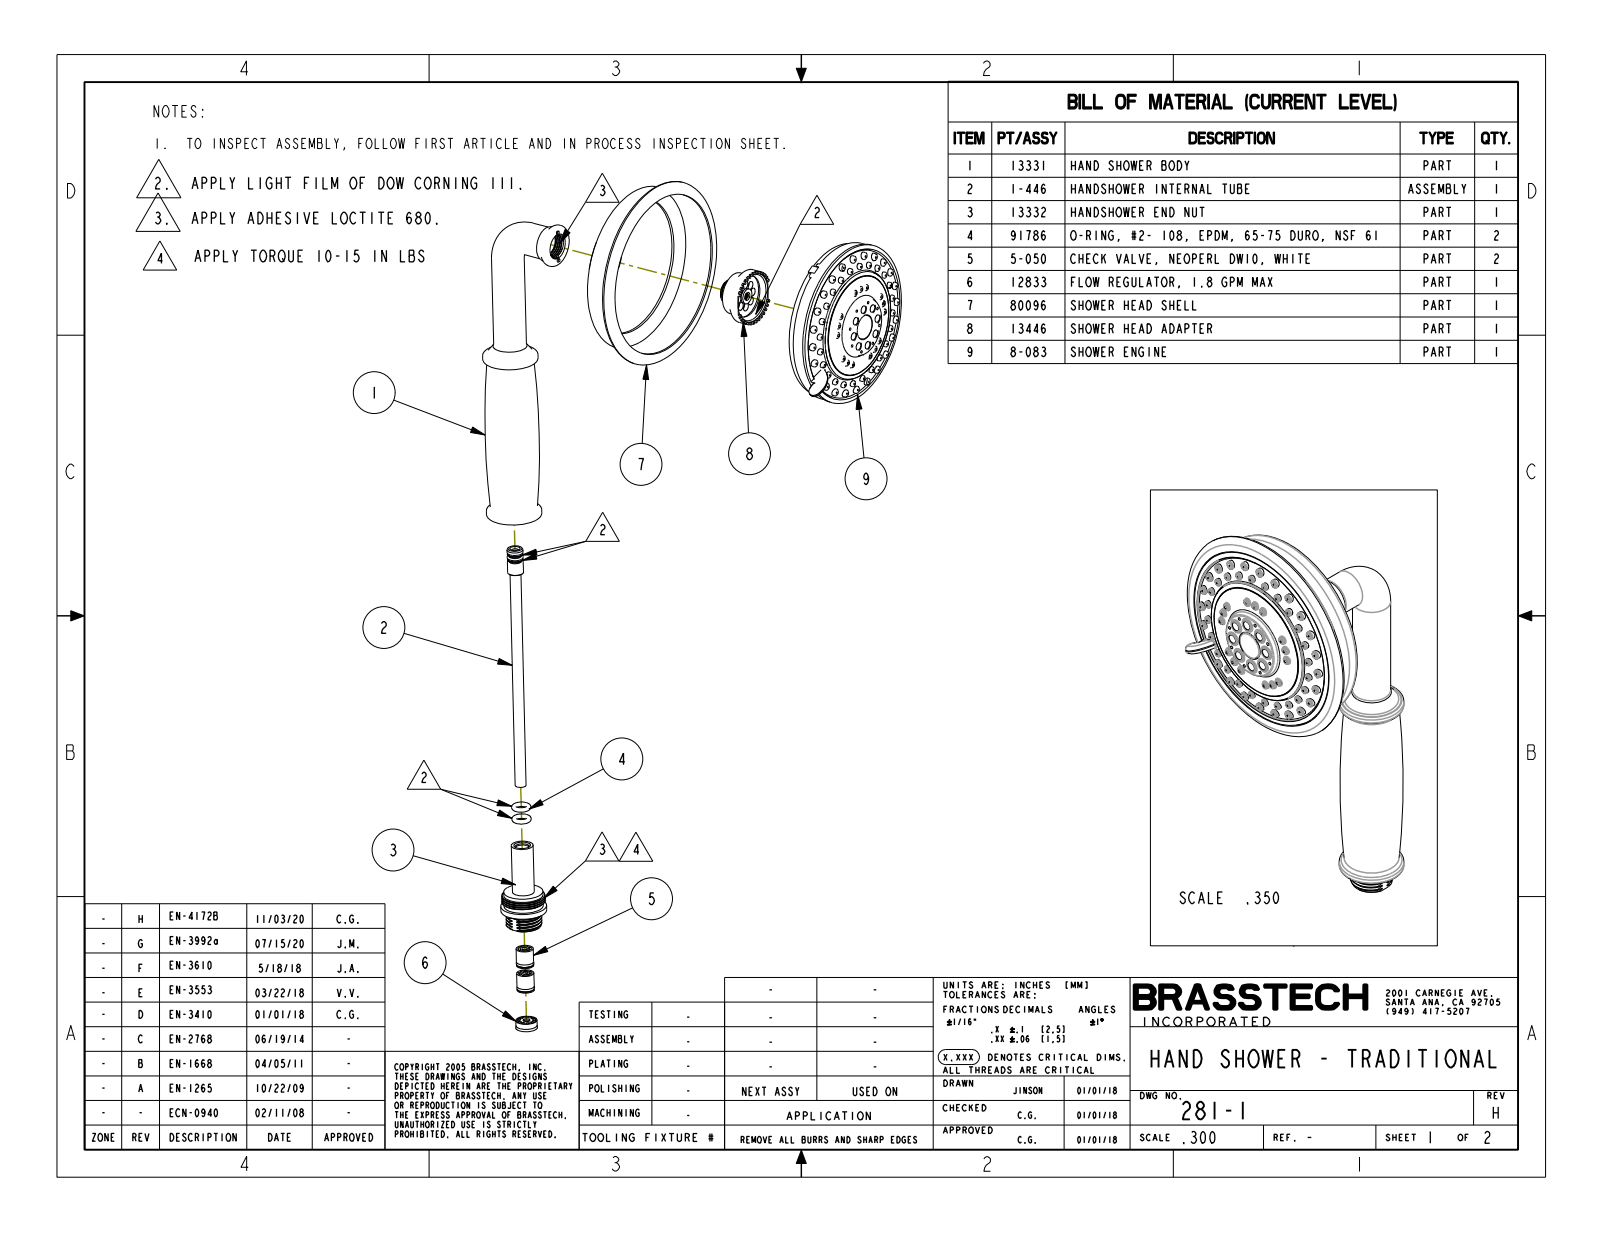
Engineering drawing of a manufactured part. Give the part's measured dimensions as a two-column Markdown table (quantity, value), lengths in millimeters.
| quantity | value |
| --- | --- |
| part name | 281-1 |
| STEP written by | CREO PARAMETRIC BY PTC INC, 2018400 (CONFIG_CONTROL_DESIGN) |
| units | millimeters |
| bodies | 1 solid, 1007 faces (98 planar, 159 cylindrical, 750 other) |
| overall size | 241.4 × 109.2 × 102.7 |
| volume | 348 200 mm³ |
| surface area | 46 910 mm² |
| round bosses / shafts (diameter × count) | 3.6 × 39, 4.2 × 23, 19.1 × 2, 96.8 × 1, 94.6 × 1, 82.3 × 1, 59 × 1, 32.3 × 1 |
| partial cylindrical surfaces (radius × count) | 0.5 × 4, 3.5 × 1, 10.4 × 1, 12 × 1, 13 × 1 |
| main face-to-face distances | 9.3, 49.6, 50, 0.5, 43.4, 6.2, 6.7, 44.9, 1.6, 4.6 |
